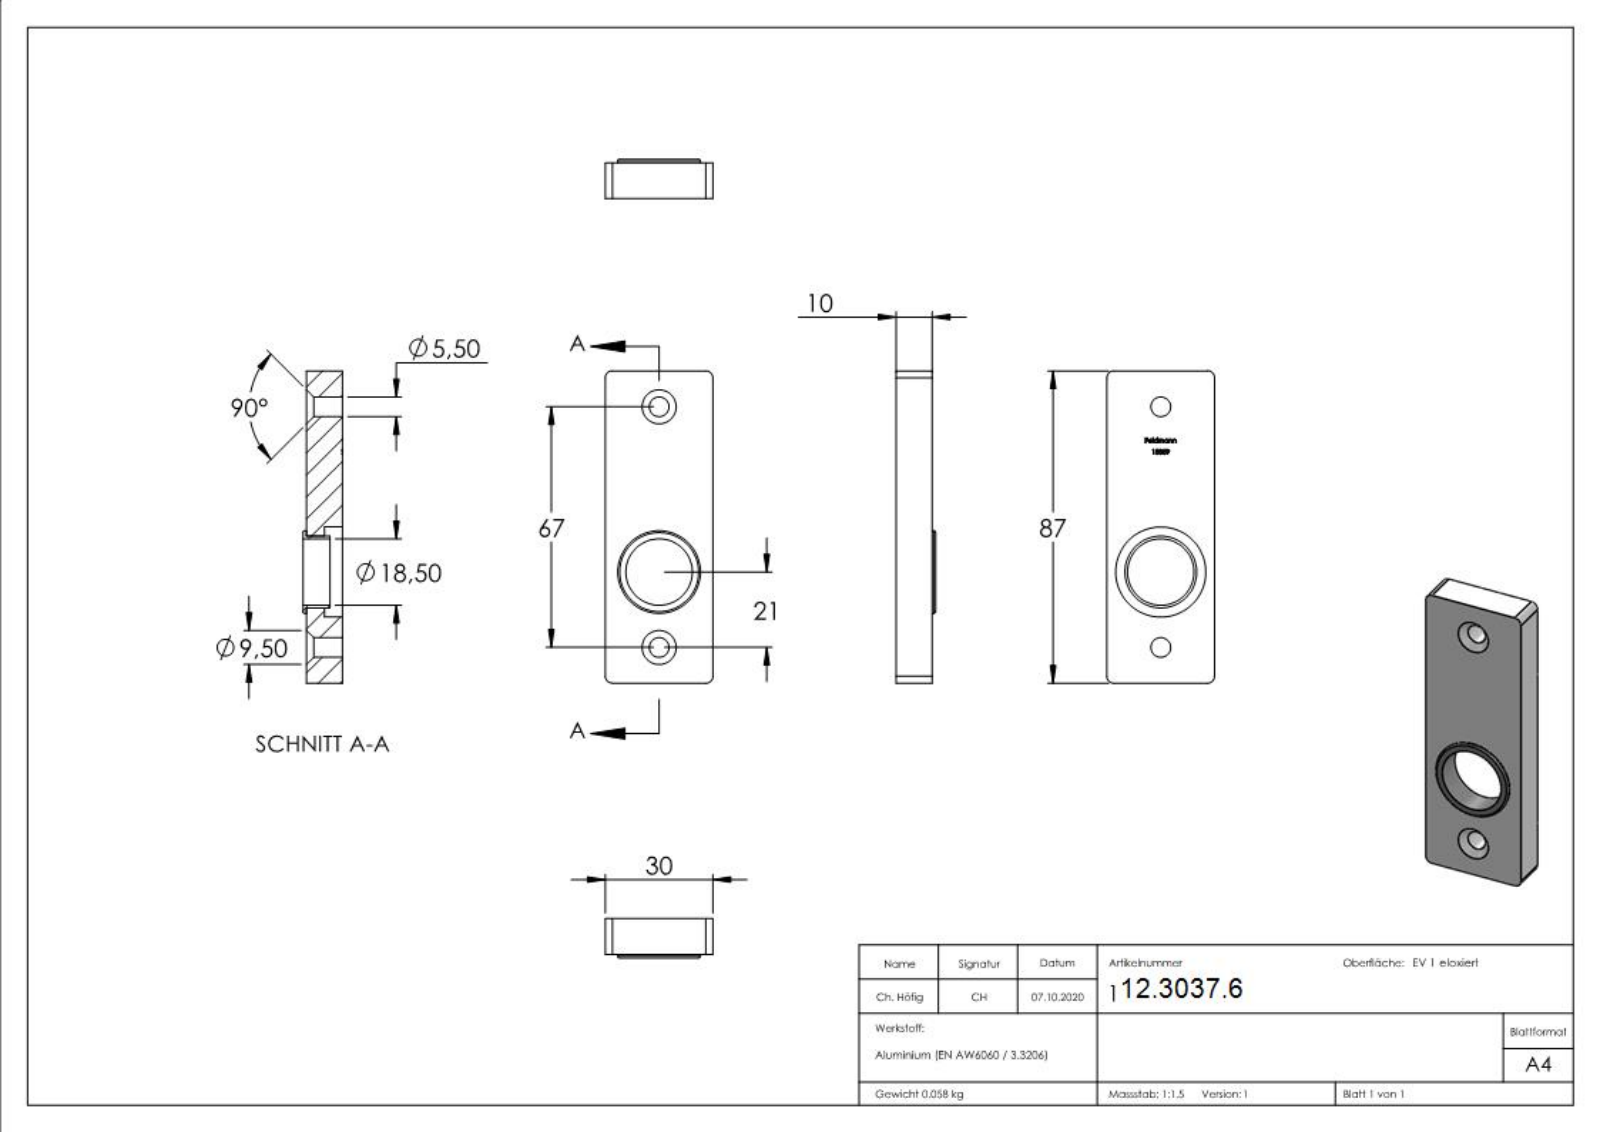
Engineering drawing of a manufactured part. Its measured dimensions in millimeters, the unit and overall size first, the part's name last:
Units: millimetres
Overall size (bounding box): 87 × 30 × 11
Round holes (diameter × count): ⌀5.5 ×2, ⌀18.5 ×1, ⌀20 ×1, ⌀25.1 ×1
Round bosses / shafts (diameter × count): ⌀23 ×1
Partial cylindrical surfaces — rounded edges, fillets, slot ends (radius × count): R2 ×4
Main face-to-face distances: 10, 30, 5, 87, 1, 11, 6, 3.5, 1.5, 6.5
Hole centre spacings: 21, 46, 67
Volume: 21 897 mm³ · Surface area: 9 021 mm²
Bodies: 2 solids, 218 faces (104 planar, 18 cylindrical, 96 other)
Part name (STEP PRODUCT): AMF Schliessblech Konfig Teil1_15859 Teil1; AMF Schliessblech Konfig Teil2; AMF Schliessblech Konfig Teil1; 15859 (+1 more)
STEP written by: SolidWorks 2018 (CONFIG_CONTROL_DESIGN)
